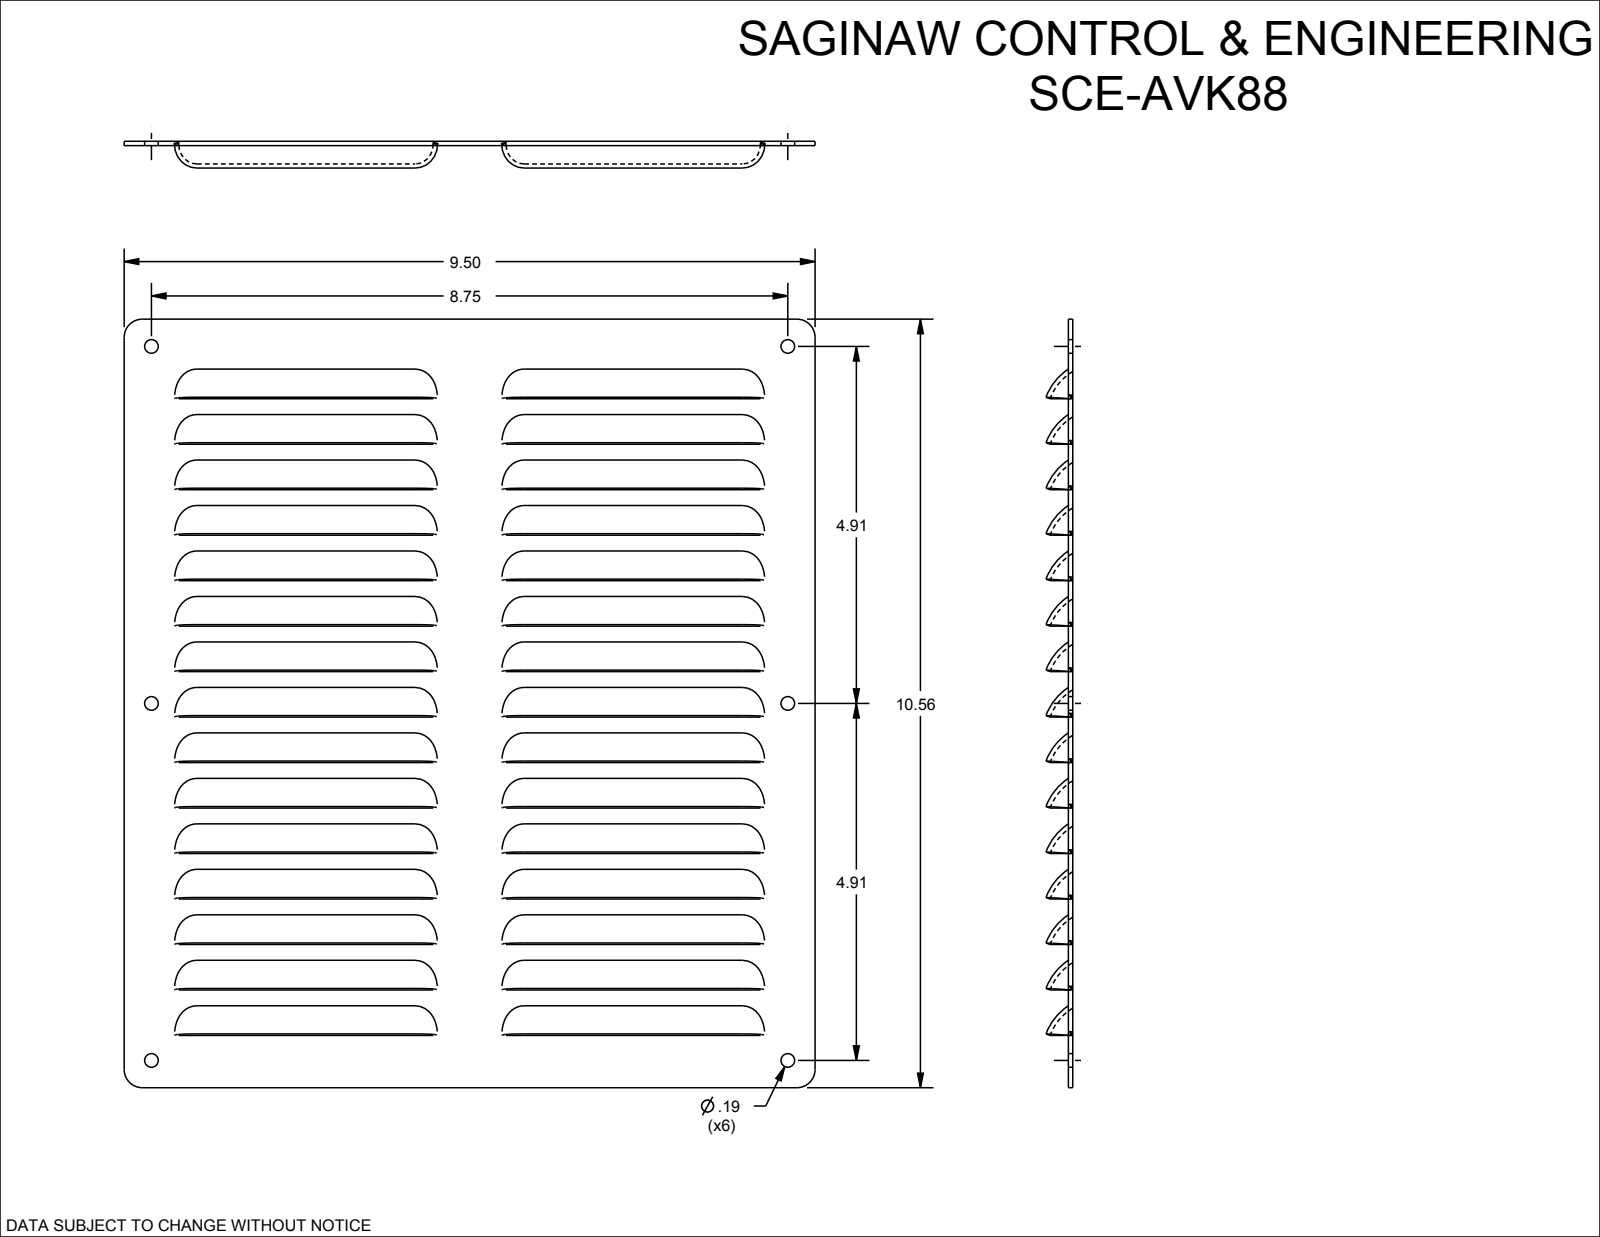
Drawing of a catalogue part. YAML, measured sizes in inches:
part_name: "SCE-AVK88"
step_written_by: "SolidWorks 2019 (CONFIG_CONTROL_DESIGN)"
units: inches
bodies: {solids: 1, faces: 442, planar: 66, cylindrical: 76, other: 300}
overall_size: [10.563, 9.5, 0.48]
volume: 6.797
surface_area: 243
round_holes:
  - {diameter: 0.187, count: 6}
partial_cylinders:
  - {radius: 0.74, count: 15}
  - {radius: 0.8, count: 15}
  - {radius: 0.25, count: 4}
face_to_face_distances: [0.06, 1.25, 1.171, 2.5, 2.343, 3.75, 3.514, 0.625, 5, 0.625]
hole_center_spacings: [4.906, 10.031, 8.75, 9.813, 13.147]
